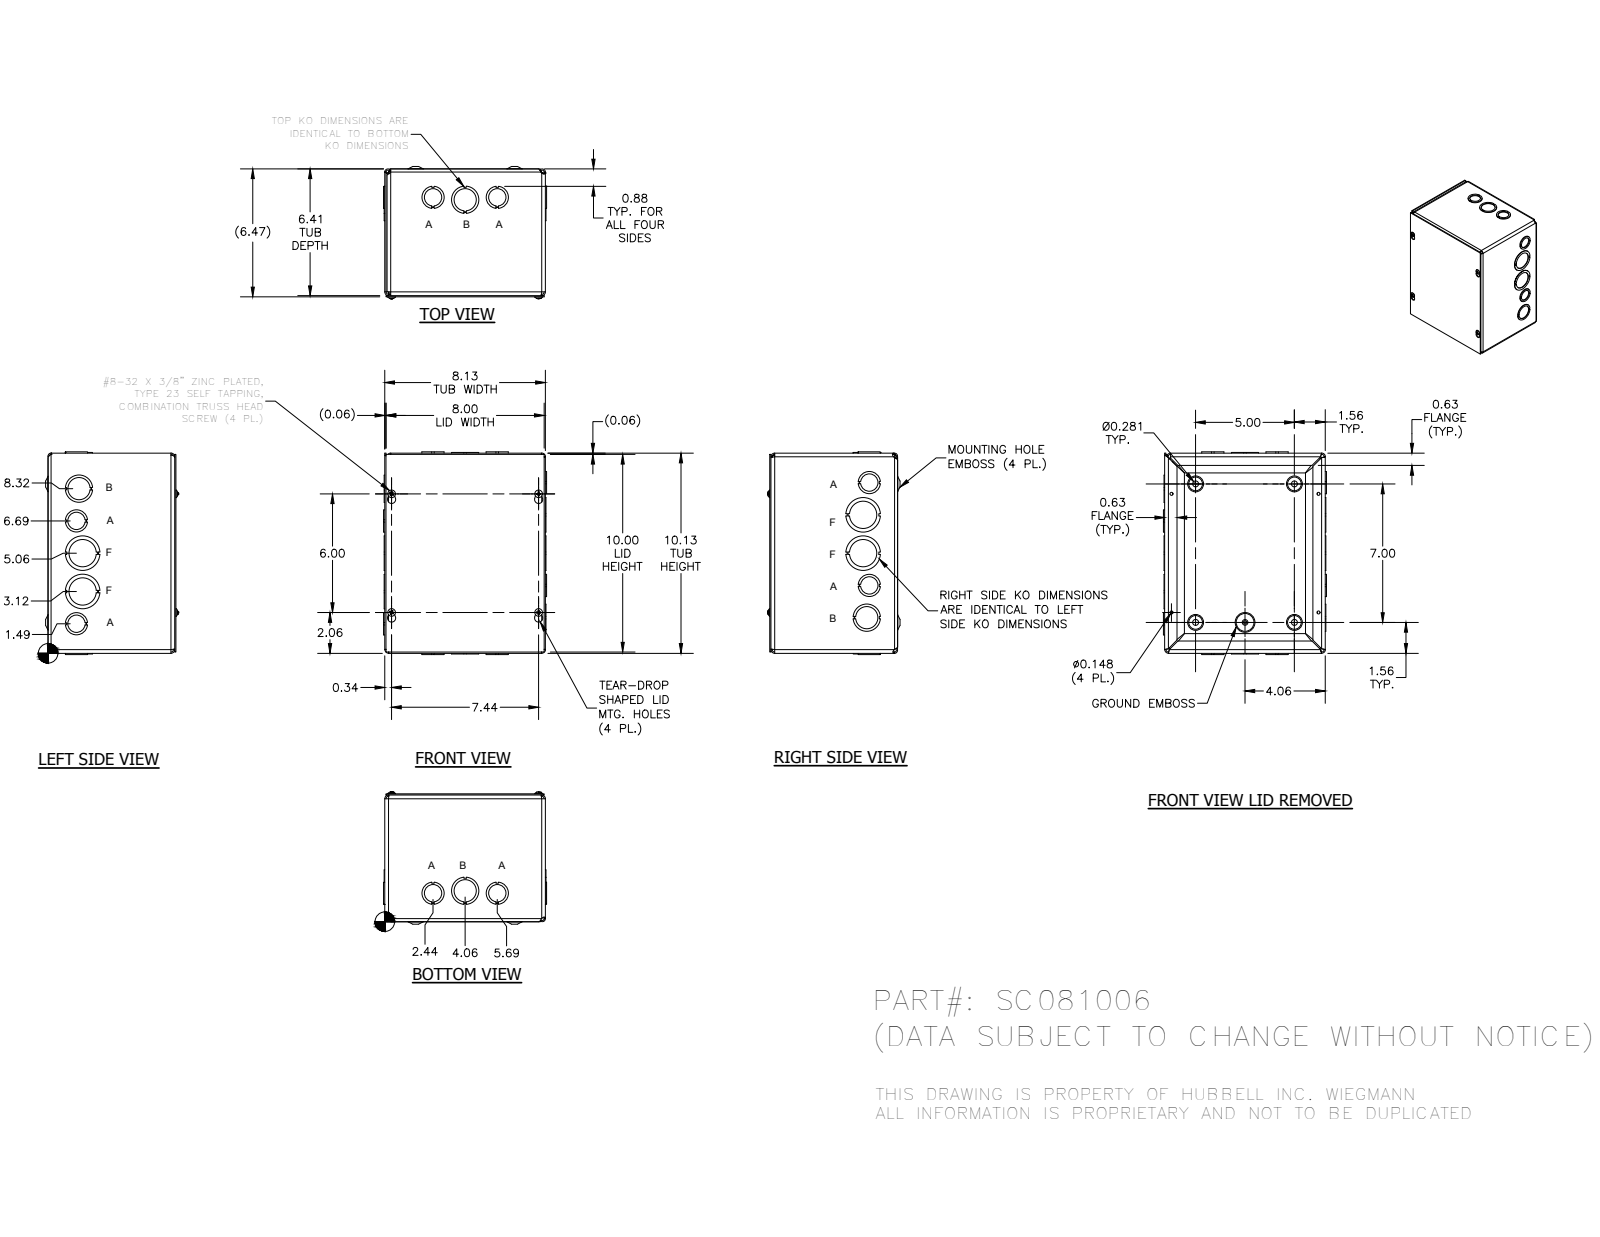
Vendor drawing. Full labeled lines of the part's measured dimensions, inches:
Part name (STEP PRODUCT): SC0810BKP; SC081006WRA; SC0810LID; 34056 (+1 more)
STEP written by: Autodesk Inventor 2014 (AUTOMOTIVE_DESIGN)
Units: inches
Bodies: 22 solids, 806 faces (485 planar, 163 cylindrical, 158 other)
Overall size (bounding box): 10.249 × 8.249 × 6.693
Round holes (diameter × count): ⌀1.125 ×9, ⌀0.875 ×6, ⌀1.375 ×6, ⌀0.148 ×4, ⌀0.3 ×4, ⌀1.75 ×3, ⌀0.165 ×1
Round bosses / shafts (diameter × count): ⌀0.384 ×4, ⌀0.164 ×4, ⌀0.228 ×1
Partial cylindrical surfaces — rounded edges, fillets, slot ends (radius × count): R0.125 ×12, R0.187 ×8, R0.055 ×4, R0.062 ×4, R0.094 ×4, R0.117 ×4, R0.124 ×4, R0.156 ×4
Main face-to-face distances: 0.062, 0.062, 6.343, 6.405, 0.063, 6.406, 6.468, 8.125, 8.063, 8.001
Hole centre spacings: 6.613, 8.996, 1.659, 1.94, 3.584, 1.317, 1.317, 1.333
